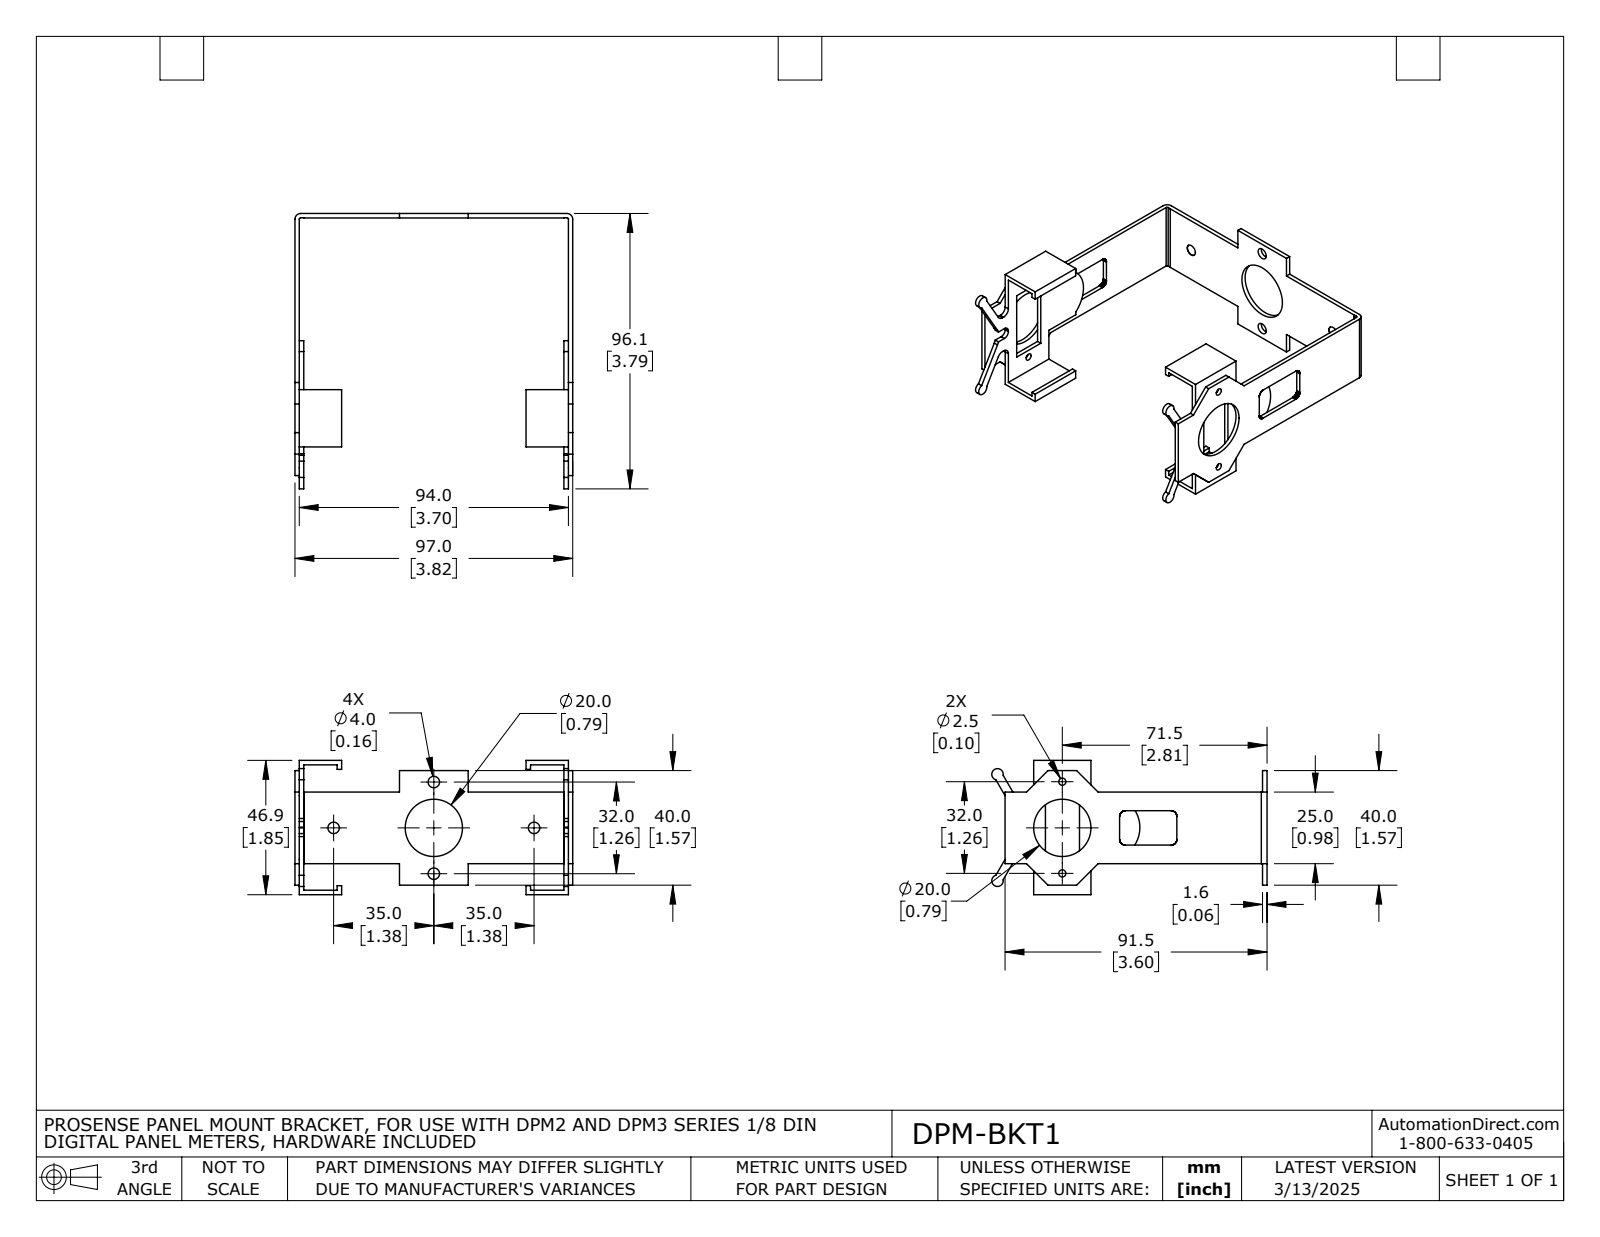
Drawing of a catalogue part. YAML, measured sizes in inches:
part_name: "DPM-BKT1"
step_written_by: "SolidWorks 2021 (AUTOMOTIVE_DESIGN)"
units: inches
bodies: {solids: 3, faces: 547, planar: 482, cylindrical: 65, other: 0}
overall_size: [3.819, 3.785, 1.846]
volume: 0.91
surface_area: 34.3
round_holes:
  - {diameter: 0.157, count: 4}
  - {diameter: 0.098, count: 2}
  - {diameter: 0.787, count: 2}
partial_cylinders:
  - {radius: 0.079, count: 4}
  - {radius: 0.093, count: 4}
  - {radius: 0.02, count: 2}
  - {radius: 0.077, count: 2}
  - {radius: 0.248, count: 1}
  - {radius: 0.444, count: 1}
face_to_face_distances: [0.062, 0.059, 3.76, 3.701, 0.121, 3.698, 3.639, 3.819, 3.577, 1.846]
hole_center_spacings: [1.515, 0.63, 1.26, 1.378, 0.625, 0.635, 2.756]
